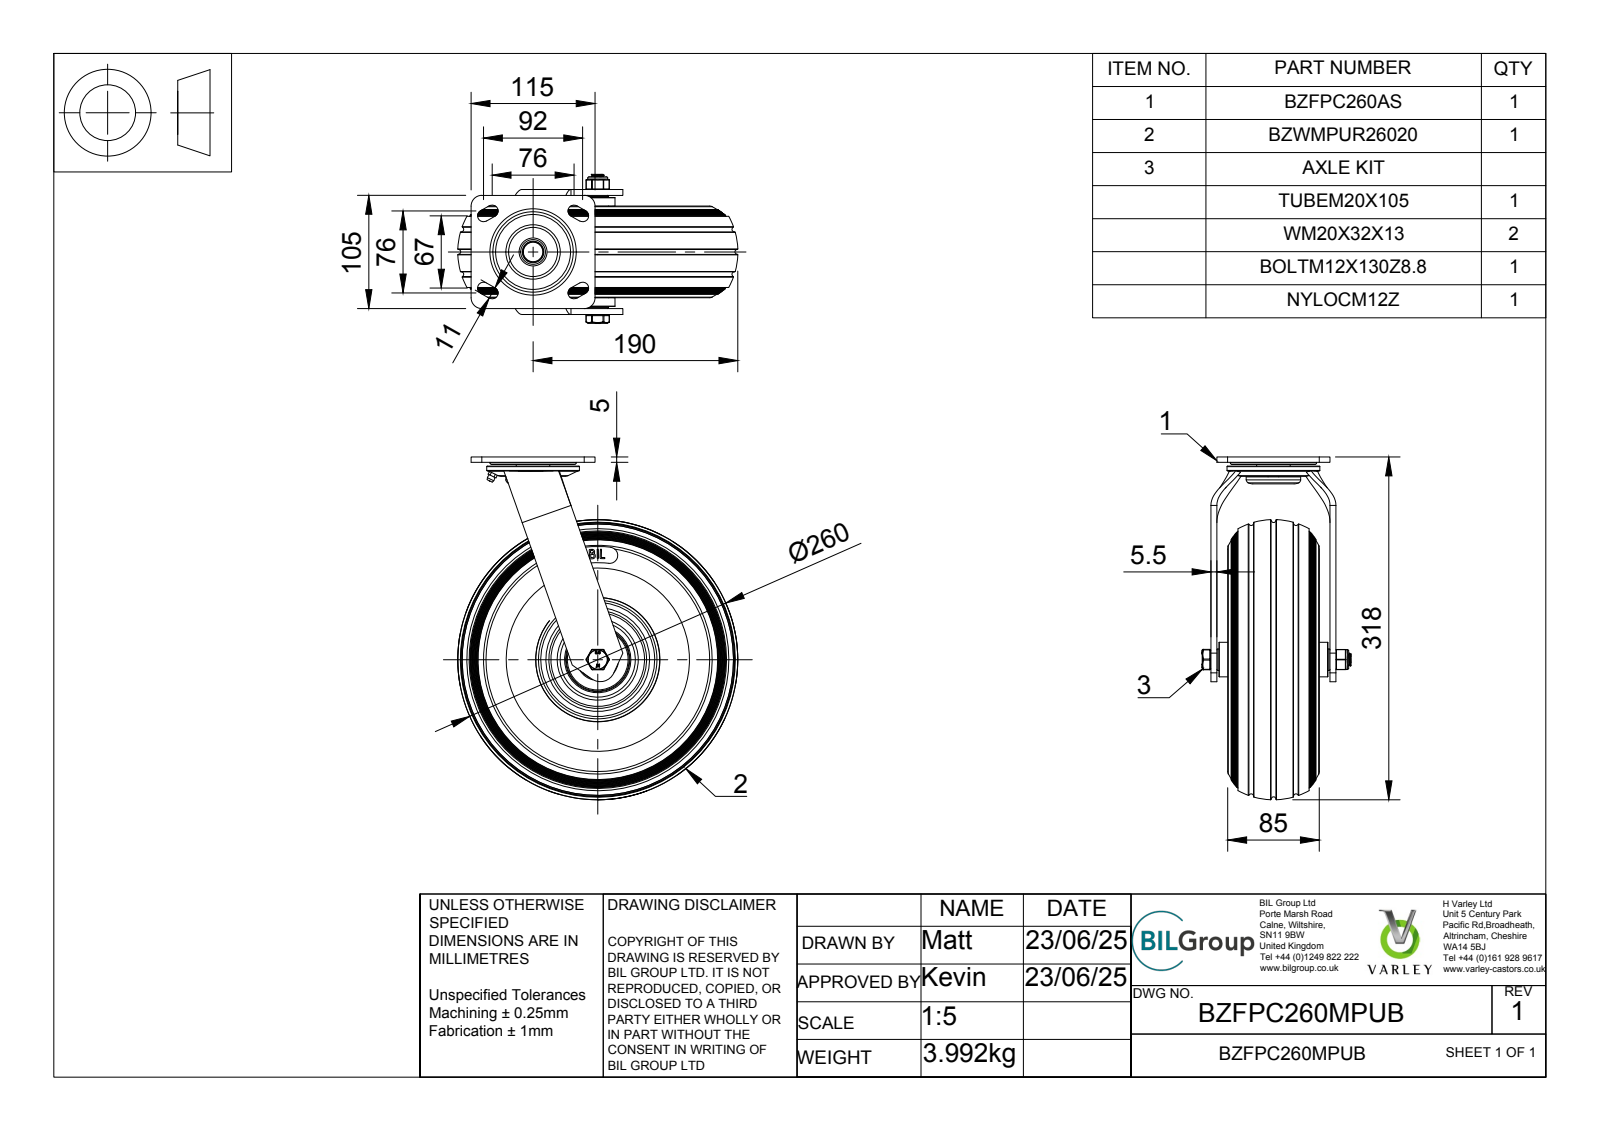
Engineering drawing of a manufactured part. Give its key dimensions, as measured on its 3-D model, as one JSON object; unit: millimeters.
{"part_name": "BZFPC260MPUB v3; BZFPC260AS v1; FABRICATED STEEL TOP PLATE; FABRICATED STEEL FORKS (+8 more)", "step_written_by": "Autodesk Translation Framework v14.10.0.0 (AUTOMOTIVE_DESIGN)", "units": "millimeters", "bodies": {"solids": 22, "faces": 647, "planar": 236, "cylindrical": 175, "other": 236}, "overall_size": [318.09, 259.89, 138.3], "volume_mm3": 3648000, "surface_area_mm2": 390827, "round_holes": [[0.8, 2], [12, 1], [12.5, 1], [13, 1], [14, 1], [20, 1], [21, 1], [22, 1], [29.8, 1], [35, 1], [98, 1], [111, 1]], "round_bosses_or_shafts": [[7.5, 8], [86, 1], [80, 1], [61.5, 1], [58, 1], [50.5, 1], [34, 1], [32.5, 1]], "partial_cylinders_radius": [[0.5, 24], [5.5, 8], [1, 6], [0.4, 4], [0.77, 4], [10, 4], [0.76, 2], [0.76, 2]], "face_to_face_distances": [5.5, 110.5, 85, 5, 94.92, 9.92, 10.08, 95.08, 105, 100.42], "hole_center_spacings": [7.55, 2.98, 7.67, 7.7]}
